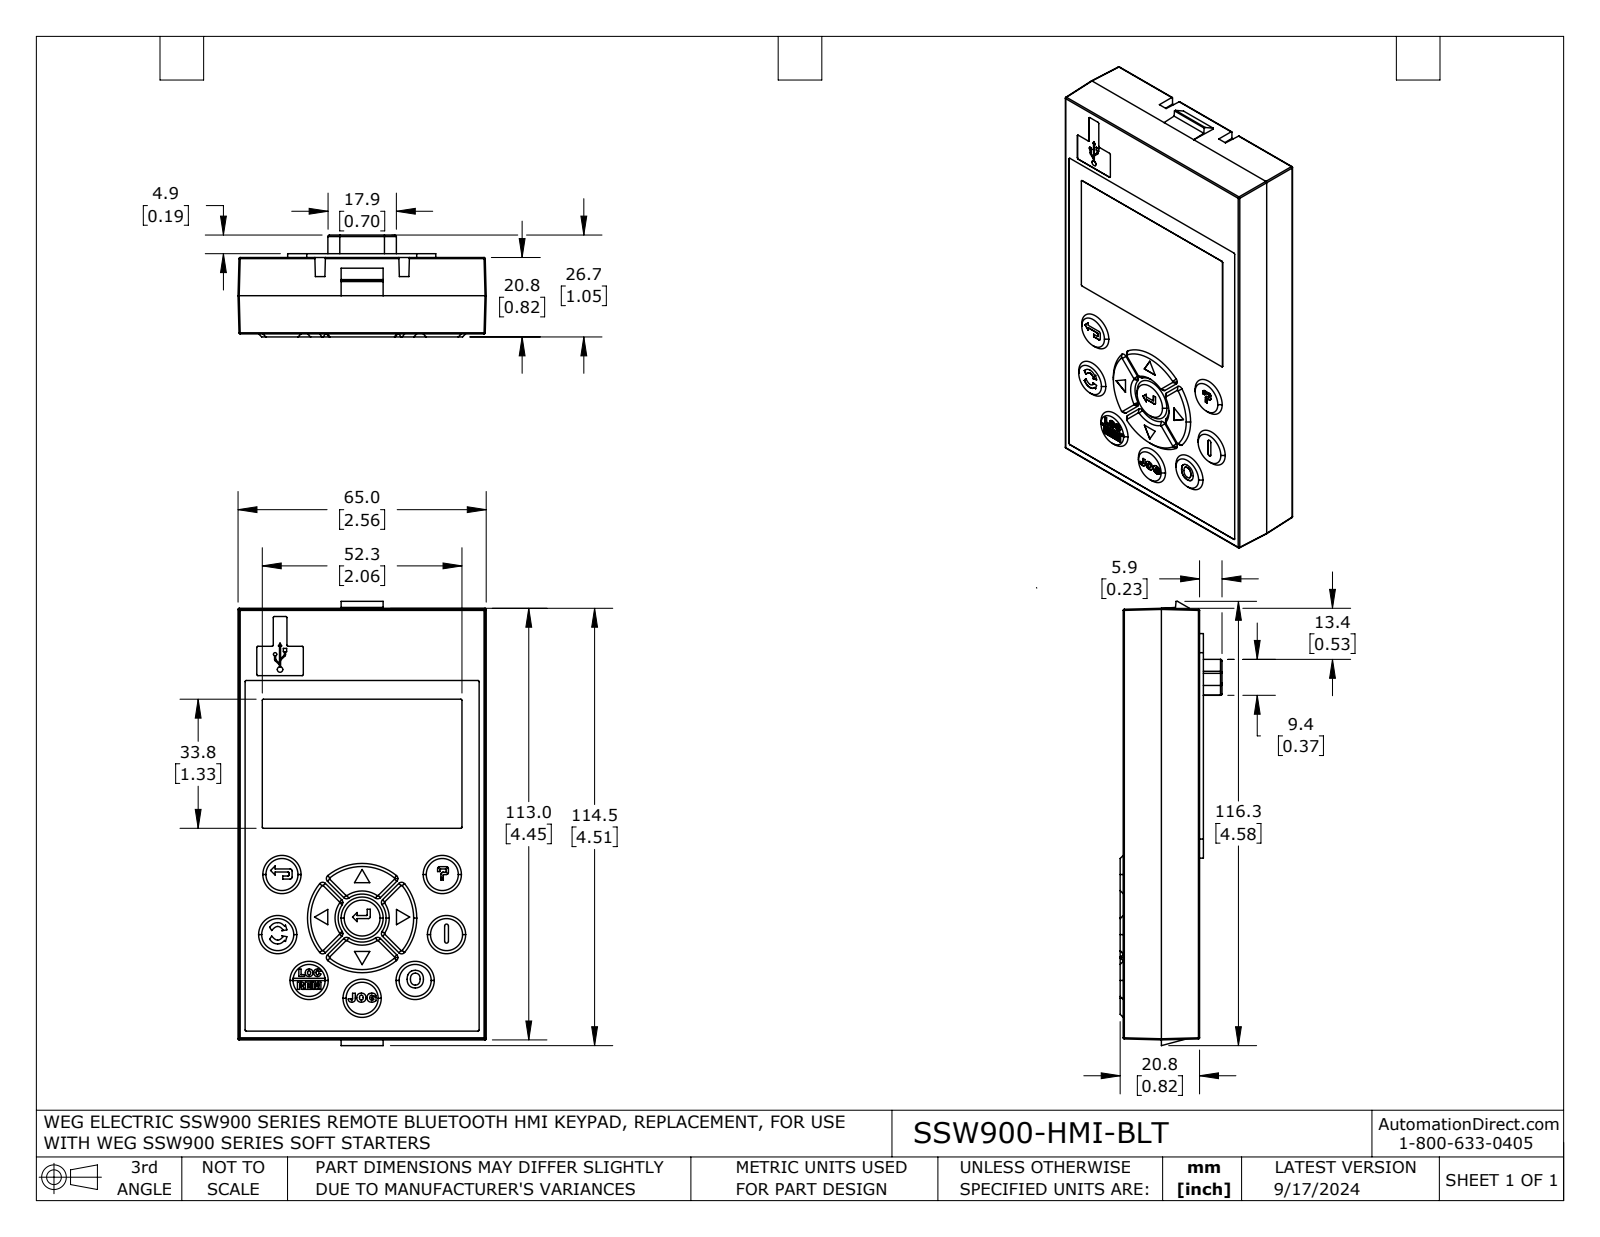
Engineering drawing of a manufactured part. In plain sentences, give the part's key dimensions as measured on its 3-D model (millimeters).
The part is named "SSW900-HMI-BLT". Its 3-D file was written by "SolidWorks 2021 (AUTOMOTIVE_DESIGN)". It is 1 solid with 579 faces: 321 planar, 100 cylindrical and 158 other. Overall it measures 116.3 by 65 by 26.7 millimeters. Its volume is 147 400 cubic millimeters and its surface area 22 890 square millimeters. Round bosses or shafts: 9 of diameter 1, 1 of diameter 1.4, 1 of diameter 0.9. Partial cylindrical surfaces (rounded edges, fillets, slot ends): 29 of radius 0.3, 5 of radius 0.5, 4 of radius 0.4, 4 of radius 0.4, 4 of radius 1, 4 of radius 2, 4 of radius 2.7, 4 of radius 3.1. The main face-to-face distances are 20, 20, 65, 113, 0.8, 20.8, 0.8, 1, 21, 21.
